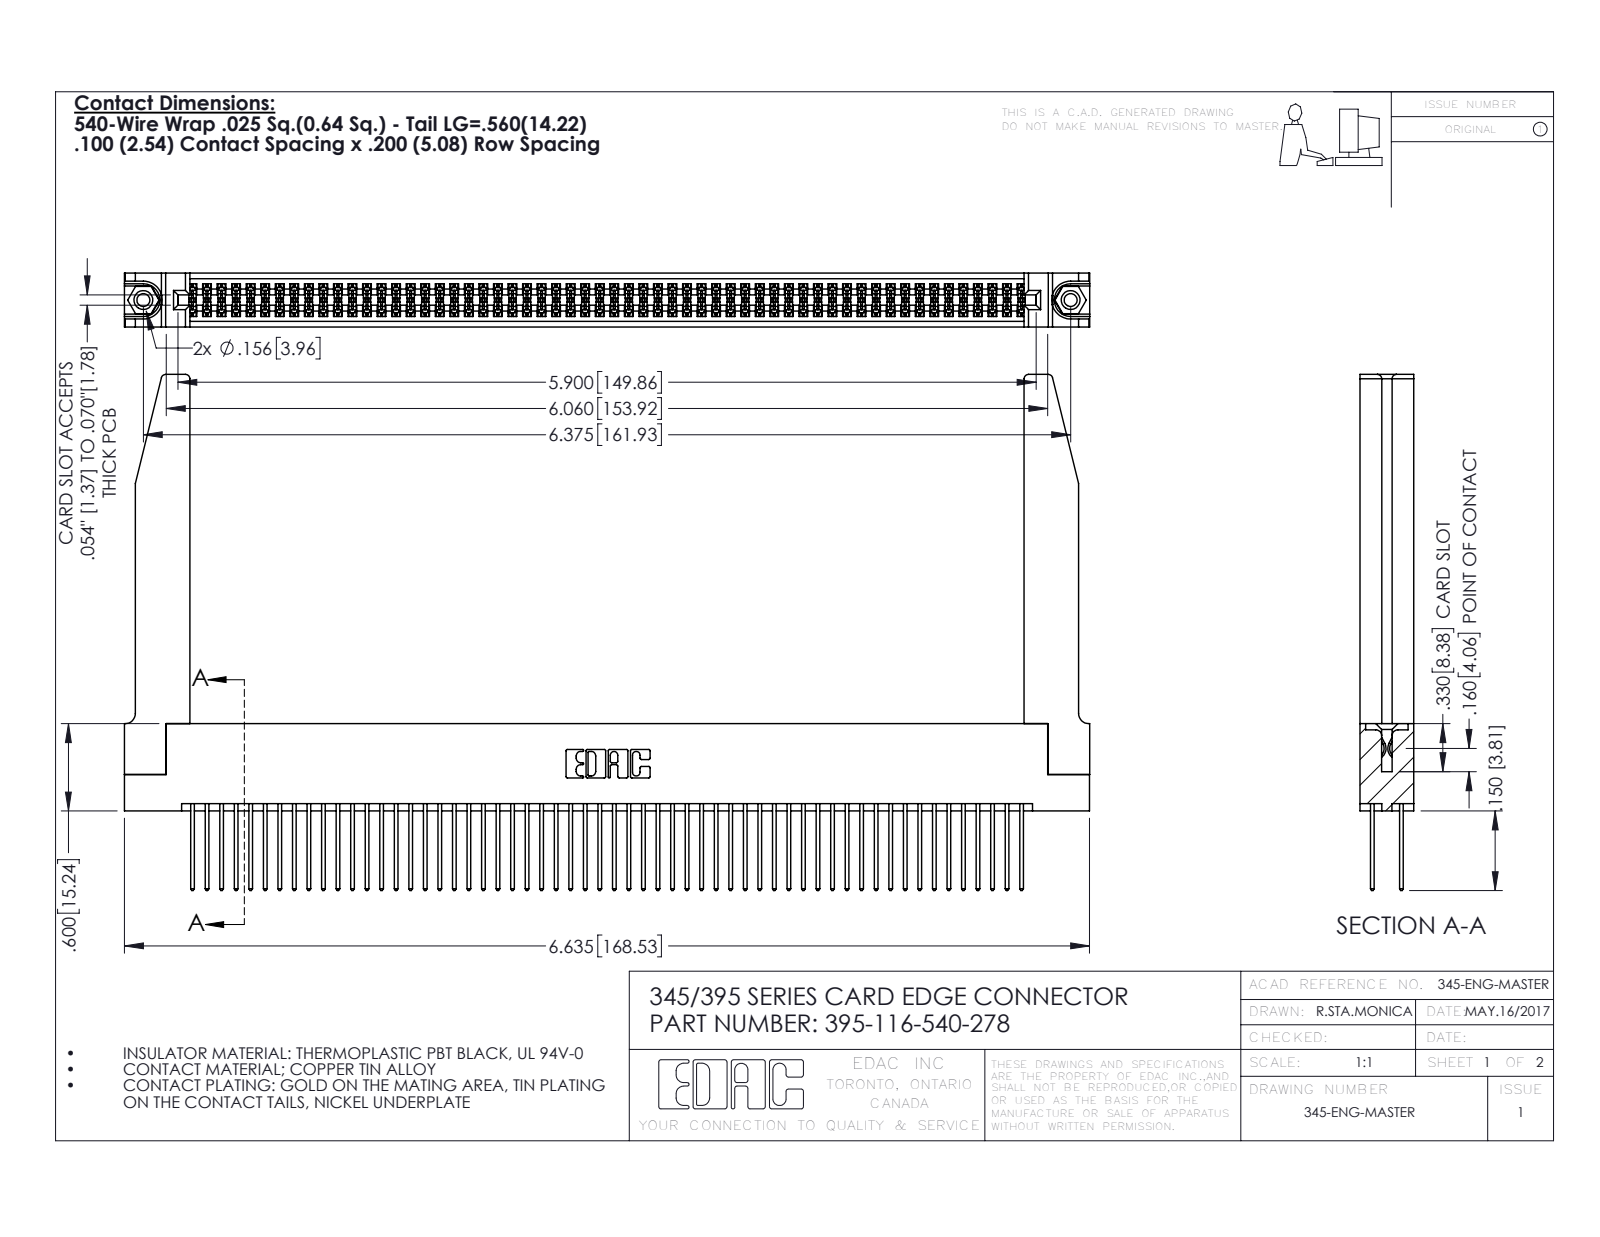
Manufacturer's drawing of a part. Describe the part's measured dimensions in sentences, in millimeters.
The part is named "345-220-078_345-220-078; 345 Part_Flush Mounting Lugs - 0.156 Dia-TH; 345-250-001_345-250-001-102; 345-292-001_345-293-140 (+1 more)". Its 3-D file was written by "SolidWorks 2016 (CONFIG_CONTROL_DESIGN)". It is 121 solids with 6160 faces: 4050 planar, 2058 cylindrical and 52 other. Overall it measures 168.6 by 90.1 by 9.4 millimeters. Its volume is 24 730 cubic millimeters and its surface area 34 260 square millimeters. Round holes: 2 of diameter 2.3, 2 of diameter 3.2, 2 of diameter 4, 1 of diameter 1.6. Round bosses or shafts: 2 of diameter 3.9. Partial cylindrical surfaces (rounded edges, fillets, slot ends): 174 of radius 0.2, 116 of radius 0.3, 22 of radius 0.3, 8 of radius 0.8, 6 of radius 0.2, 6 of radius 0.8, 3 of radius 0.7, 2 of radius 0.4. The main face-to-face distances are 1.8, 7.6, 9.4, 5.1, 2.5, 6.9, 0.6, 5.7, 4.4, 3.8. The hole center spacings are 6.9, 155.9, 161.9.
